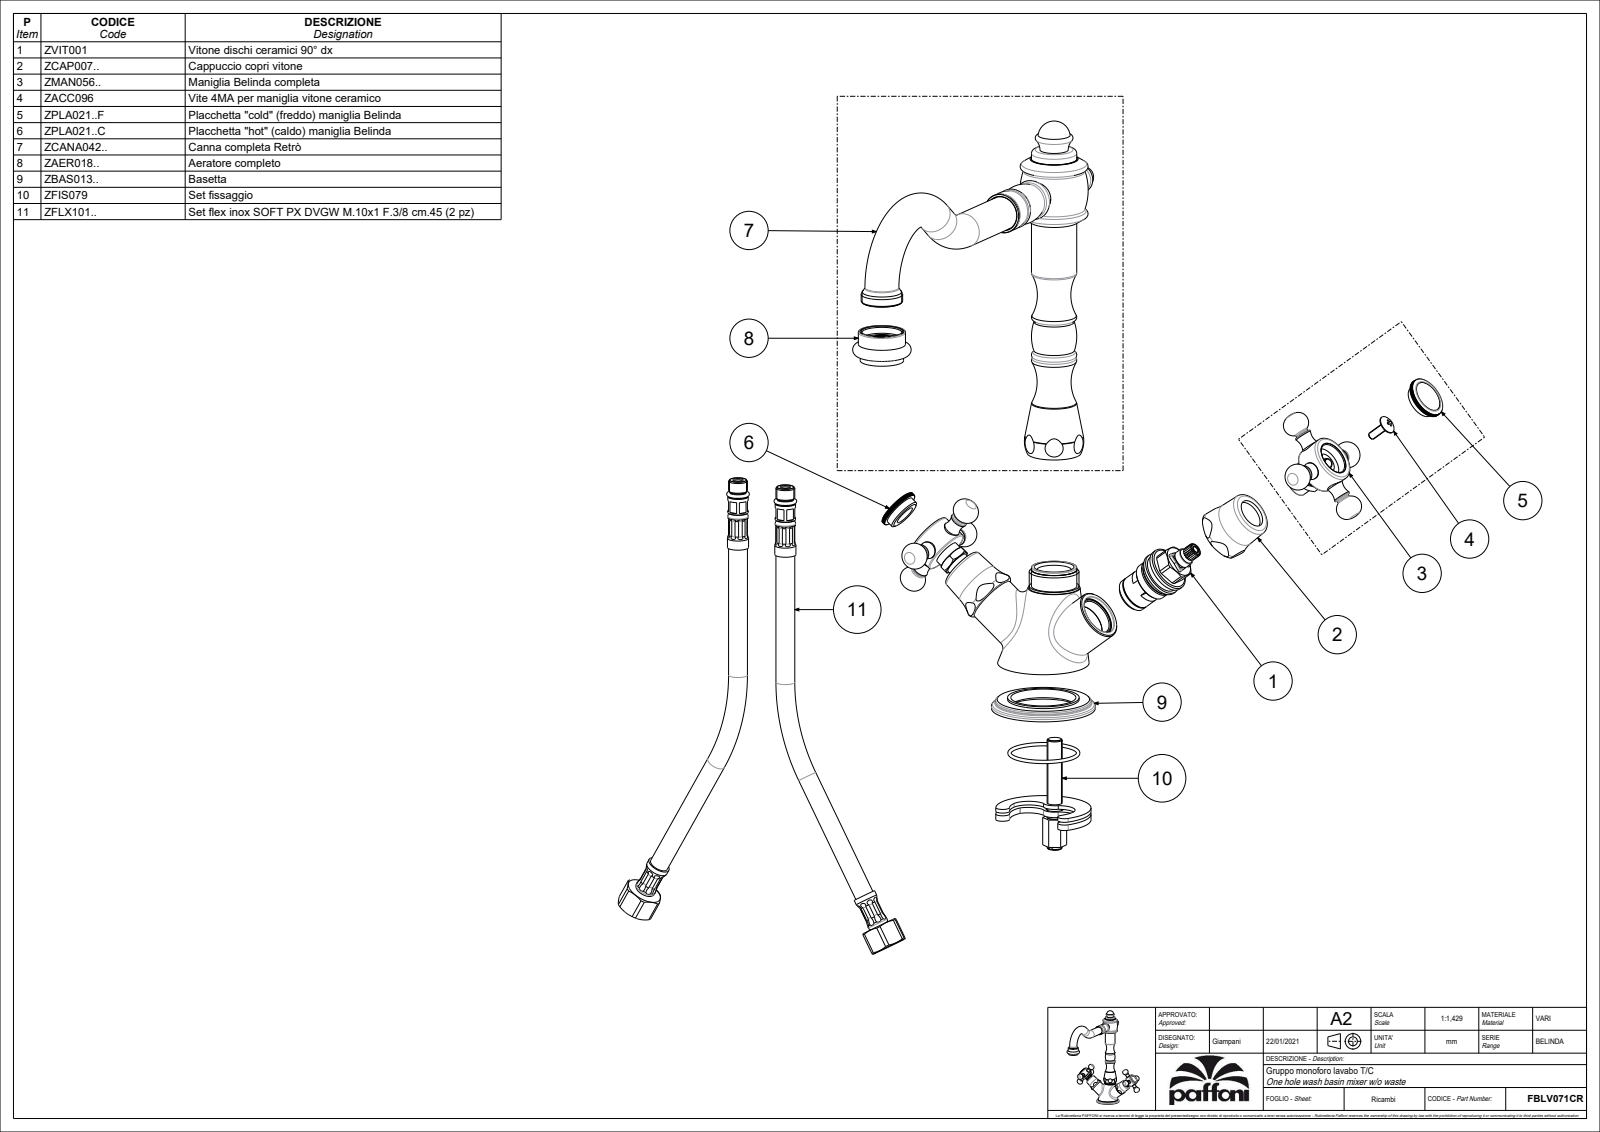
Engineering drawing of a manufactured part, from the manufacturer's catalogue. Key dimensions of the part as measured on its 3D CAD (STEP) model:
Part name (STEP PRODUCT): FBLV071CR
STEP written by: CREO PARAMETRIC BY PTC INC, 2020044 (CONFIG_CONTROL_DESIGN)
Units: millimetres
Bodies: 3 solids, 1325 faces (575 planar, 392 cylindrical, 358 other)
Overall size (bounding box): 234.73 × 229.4 × 175.57
Volume: 243 597 mm³ · Surface area: 72 165 mm²
Round holes (diameter × count): ⌀9 ×4, ⌀11 ×2, ⌀15.5 ×2, ⌀18 ×2, ⌀19 ×2, ⌀21 ×2, ⌀21.5 ×2, ⌀22.8 ×2, ⌀25.5 ×2, ⌀6 ×1, ⌀6.8 ×1, ⌀10 ×1
Round bosses / shafts (diameter × count): ⌀9 ×6, ⌀7 ×6, ⌀25 ×3, ⌀26.3 ×2, ⌀18 ×2, ⌀14 ×2, ⌀13 ×2, ⌀55 ×1
Partial cylindrical surfaces — rounded edges, fillets, slot ends (radius × count): R3.5 ×2, R11 ×2
Main face-to-face distances: 5, 4.98, 2, 1.3, 57.21, 155.6, 11.4, 160.6, 160.58, 45.81
Hole centre spacings: 7, 13.38, 13.89, 0.6, 11.4, 12, 14
